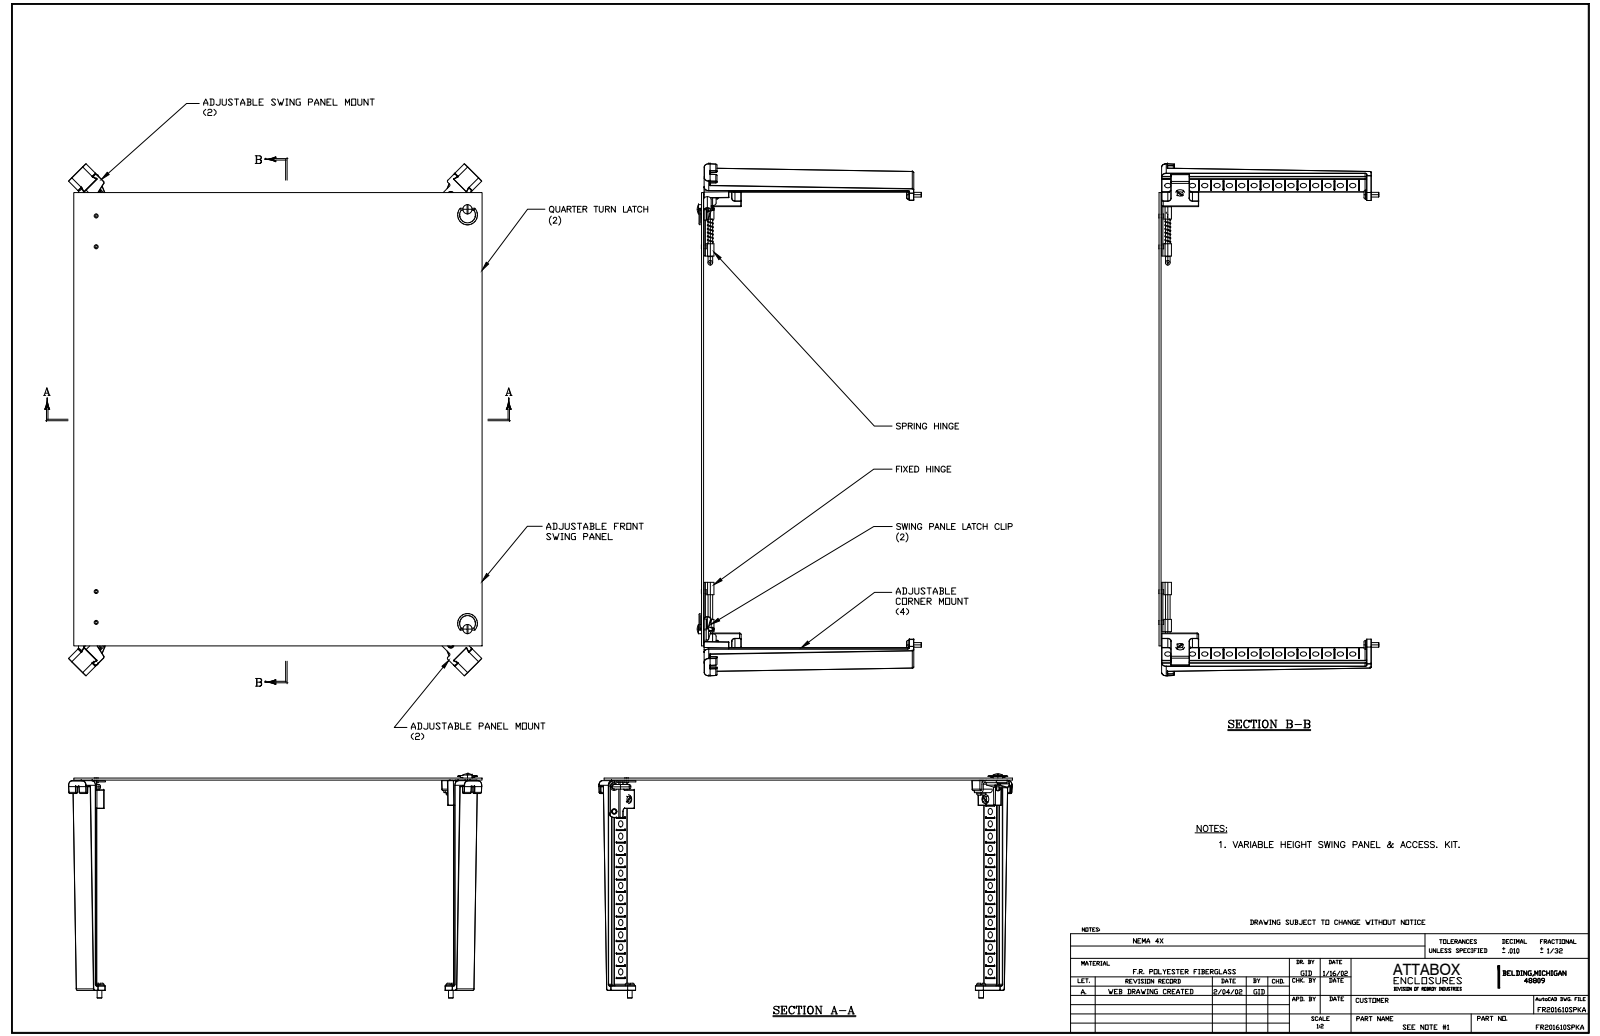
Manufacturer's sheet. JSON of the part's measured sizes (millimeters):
{"part_name": "FR201610SPKA", "step_written_by": "SolidWorks 2019 (AUTOMOTIVE_DESIGN)", "units": "millimeters", "bodies": {"solids": 48, "faces": 2737, "planar": 1414, "cylindrical": 513, "other": 810}, "overall_size": [527.2, 425.5, 221.1], "volume_mm3": 642900, "surface_area_mm2": 519400, "round_holes": [[6.4, 68], [4, 6], [6.4, 6], [1.3, 4], [3.6, 4], [3.7, 4], [5.5, 4], [5.6, 4], [7.9, 3], [3.9, 2], [5, 2], [8.9, 2]], "round_bosses_or_shafts": [[4.8, 10], [9.5, 6], [6.2, 6], [11, 4], [8, 4], [4.1, 4], [2, 4], [4.7, 3]], "partial_cylinders_radius": [[0.3, 212], [1.5, 40], [1.6, 12], [0.6, 8], [3.3, 8], [1.6, 6], [1.2, 4], [3.2, 4]], "face_to_face_distances": [2, 610.1, 25.4, 256.4, 353.7, 281.8, 328.3, 71.8, 5.2, 615.3], "hole_center_spacings": [12.7, 73, 25.4, 76.2, 38.1, 81.3, 50.8, 88]}
